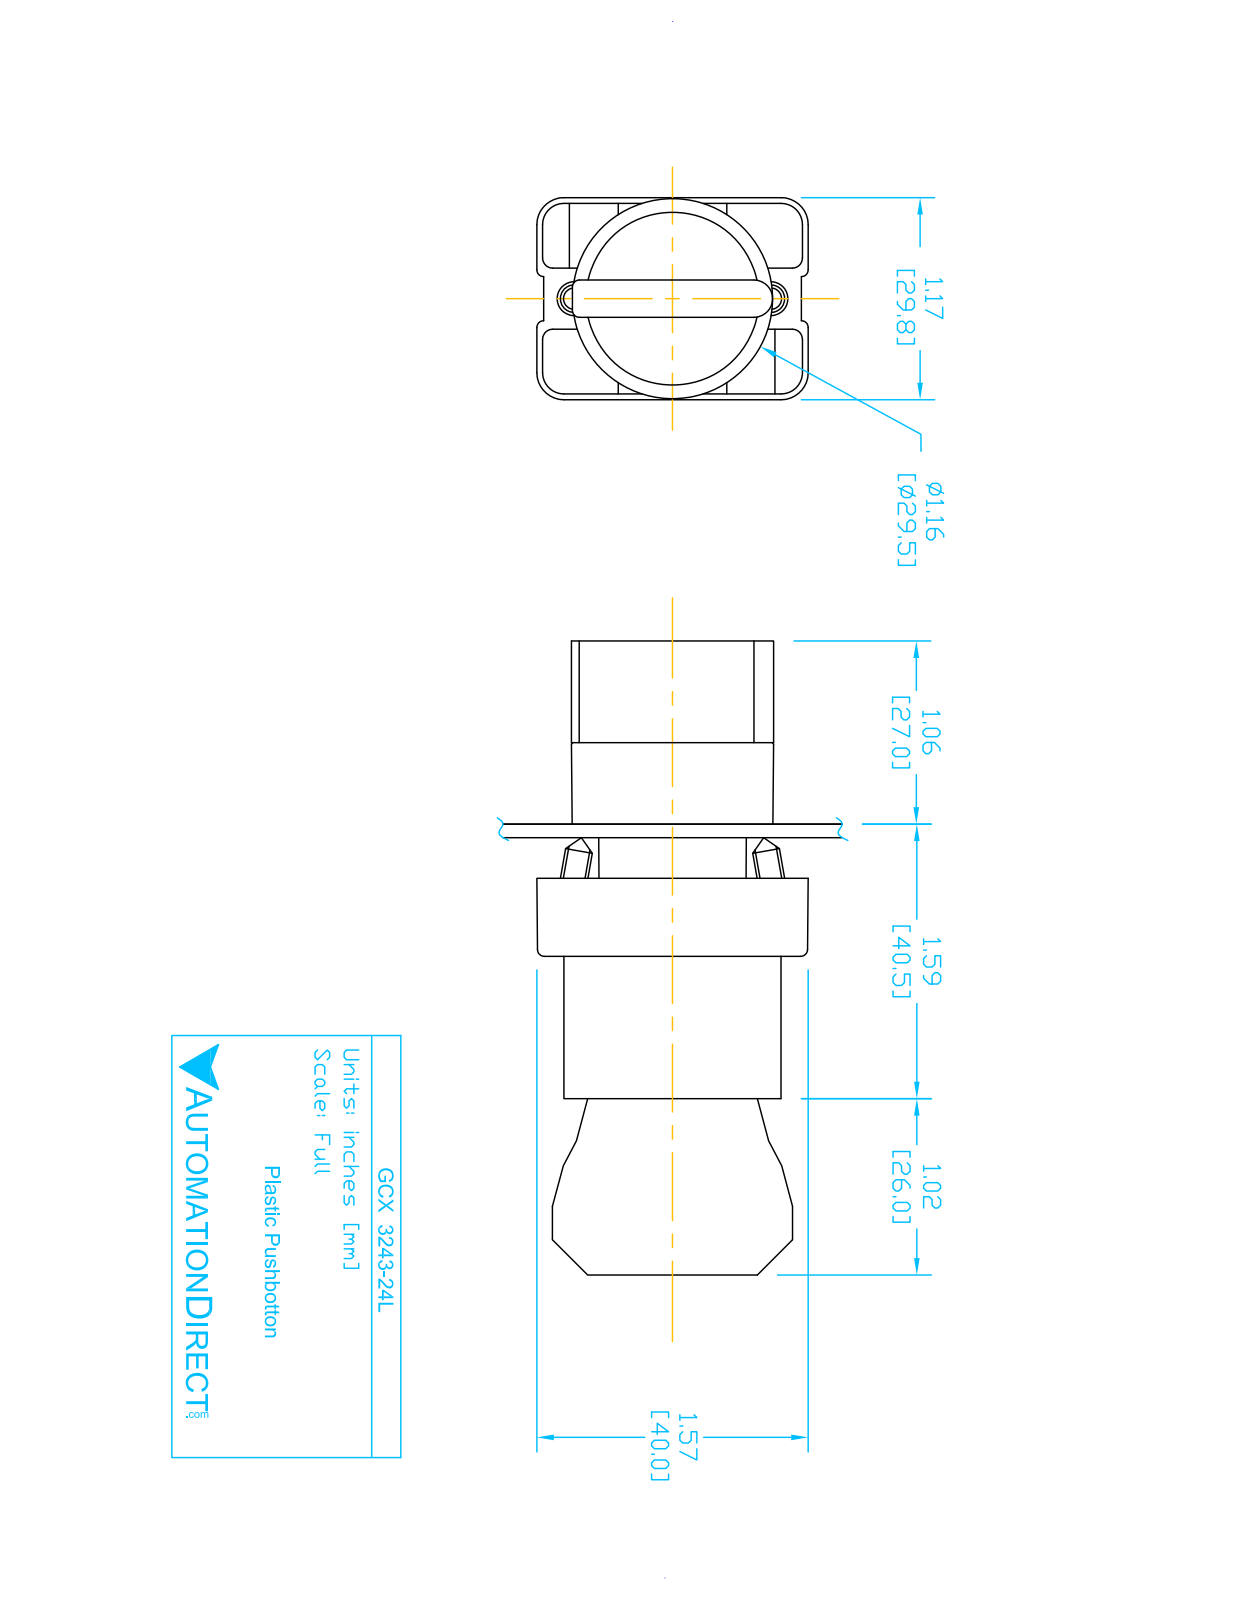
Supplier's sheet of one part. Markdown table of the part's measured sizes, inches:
| quantity | value |
| --- | --- |
| part name | ECX3029-2; GCX3243L OPERATOR; GCX3243-24L; ECX1050 (+1 more) |
| STEP written by | SolidWorks 2016 (AUTOMOTIVE_DESIGN) |
| units | inches |
| bodies | 8 solids, 445 faces (263 planar, 151 cylindrical, 31 other) |
| overall size | 3.653 × 1.581 × 1.177 |
| volume | 2.799 in³ |
| surface area | 39 in² |
| round holes (diameter × count) | 0.079 × 2, 0.124 × 2, 0.13 × 2, 0.087 × 1, 0.197 × 1, 0.469 × 1, 0.878 × 1, 0.888 × 1, 1.024 × 1 |
| round bosses / shafts (diameter × count) | 0.157 × 4, 1.175 × 1, 1.004 × 1, 0.945 × 1, 0.856 × 1, 0.78 × 1, 0.504 × 1 |
| partial cylindrical surfaces (radius × count) | 0.059 × 24, 0.041 × 12, 0.124 × 12, 0.157 × 12, 0.039 × 9, 0.128 × 2, 0.02 × 1, 0.063 × 1 |
| main face-to-face distances | 0.827, 2.02, 1.193, 0.579, 1.244, 1.171, 0.472, 0.469, 0.031, 0.033 |
| hole center spacings | 0.236, 0.544, 0.472, 0.49 |
